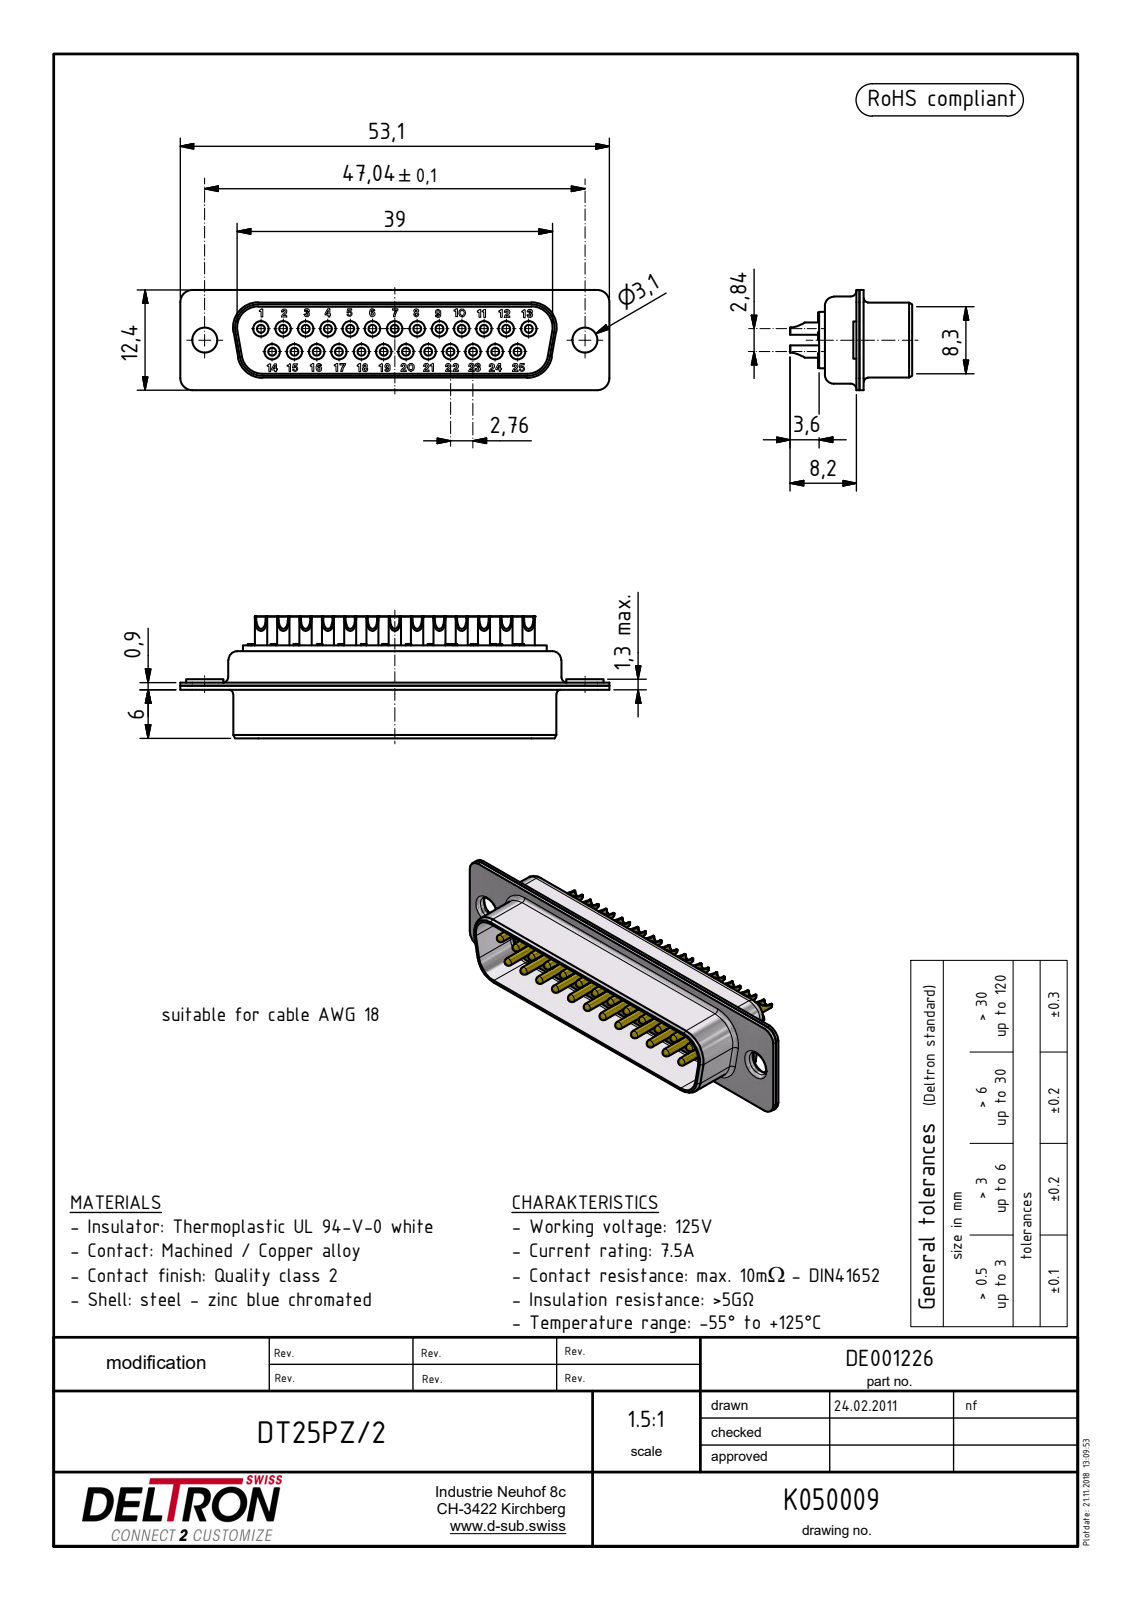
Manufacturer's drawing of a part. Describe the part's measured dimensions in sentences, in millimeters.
The part is named "N00405_BG; R+B00919_BG; R+B00128_BG; R+B00123_BG (+1 more)". Its 3-D file was written by "Autodesk Inventor 2015 (AUTOMOTIVE_DESIGN)". It is 28 solids with 1594 faces: 836 planar, 443 cylindrical and 315 other. Overall it measures 53.1 by 15.1 by 12.4 millimeters. Its volume is 2 481 cubic millimeters and its surface area 7 064 square millimeters. Round holes: 25 of diameter 1.2, 25 of diameter 1.92, 25 of diameter 2.3, 6 of diameter 0.34, 4 of diameter 0.24, 4 of diameter 0.28, 2 of diameter 3.1, 2 of diameter 4.06. Round bosses or shafts: 25 of diameter 2.23, 25 of diameter 1.96, 25 of diameter 1.94, 25 of diameter 1.6, 25 of diameter 1.6, 25 of diameter 1.5, 25 of diameter 1, 2 of diameter 4.6. Partial cylindrical surfaces (rounded edges, fillets, slot ends): 26 of radius 0.25, 12 of radius 2, 8 of radius 0.7, 8 of radius 1, 8 of radius 1.1, 6 of radius 0.34, 4 of radius 0.5, 4 of radius 1.2. The main face-to-face distances are 0.5, 0.4, 8.8, 0.65, 8.3, 8.95, 9.45, 0.6, 0.35, 1.3. The hole center spacings are 2.76, 5.52, 8.28, 3.16, 5.02, 11.04, 7.46, 13.8.
